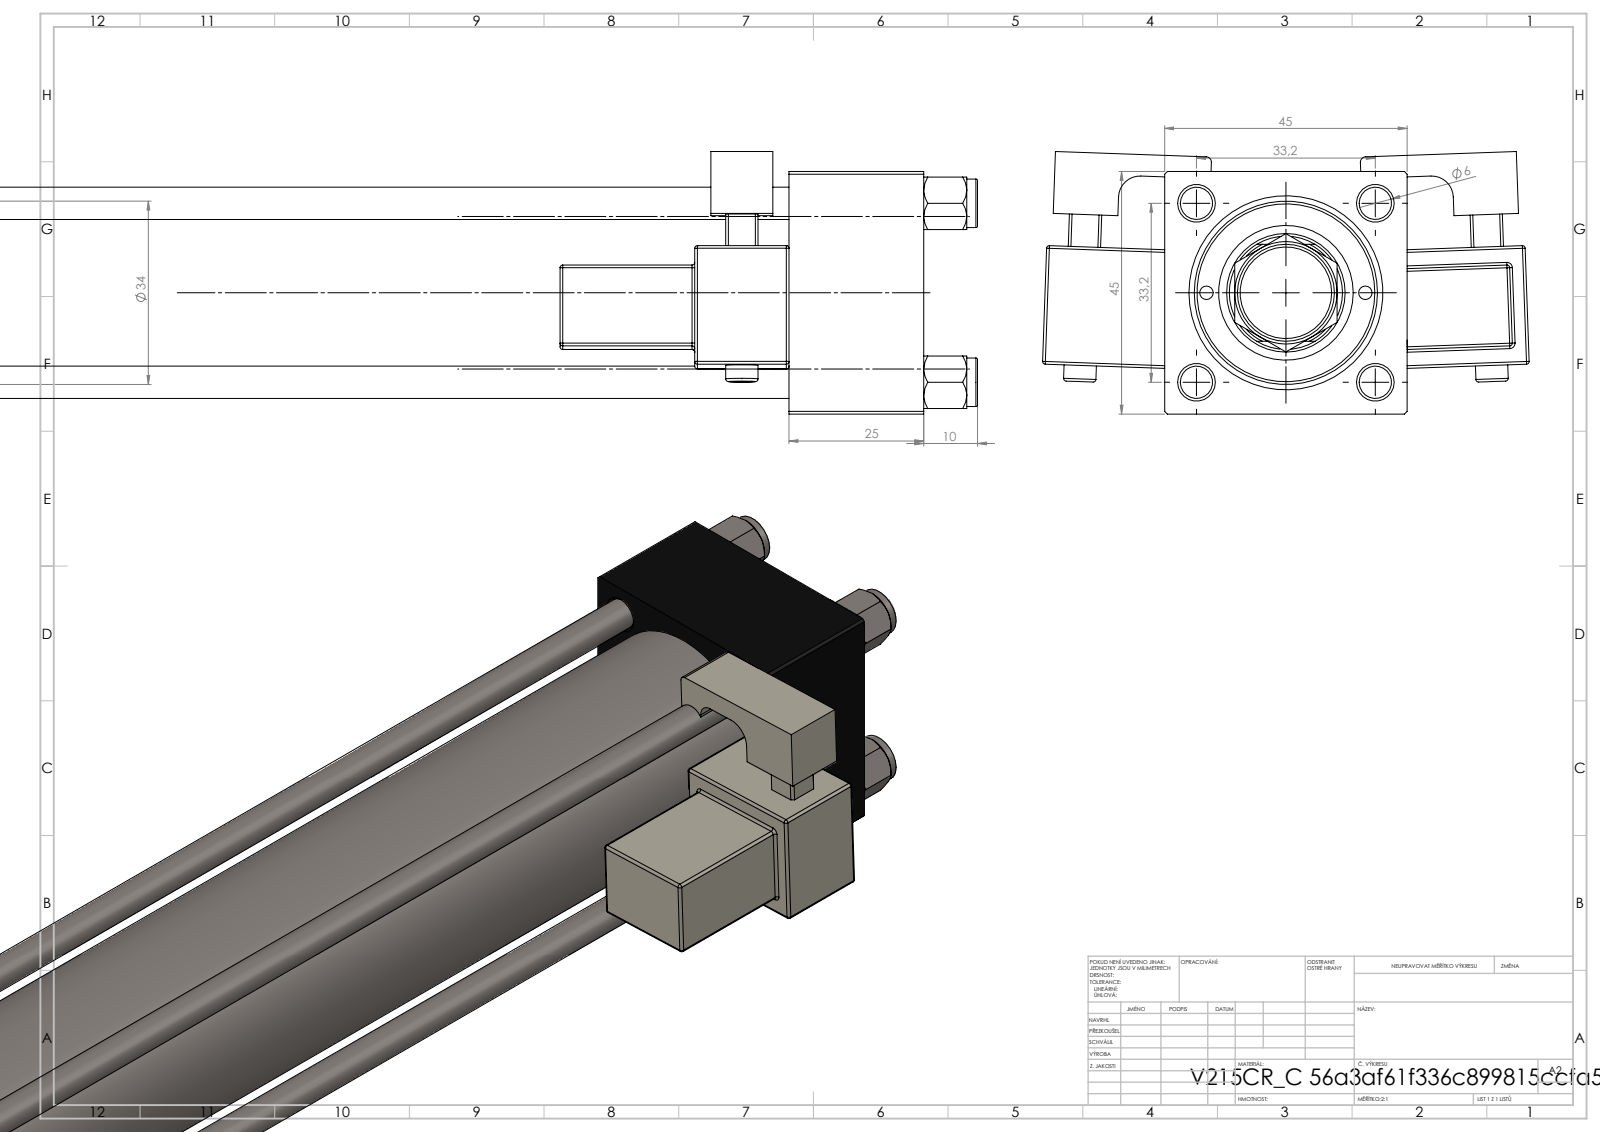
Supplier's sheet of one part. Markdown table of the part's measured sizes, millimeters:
| quantity | value |
| --- | --- |
| part name | V215CR_VCP_C; V215_VC_A; MFA; V215CR_C_TYCINKA (+3 more) |
| STEP written by | SolidWorks 2019 (CONFIG_CONTROL_DESIGN) |
| units | millimeters |
| bodies | 14 solids, 1363 faces (605 planar, 154 cylindrical, 604 other) |
| overall size | 371 × 90.31 × 48.72 |
| volume | 406 576 mm³ |
| surface area | 151 864 mm² |
| round holes (diameter × count) | 6 × 4, 2.5 × 2, 7 × 2, 13.16 × 2, 20 × 2, 10.5 × 1, 22 × 1, 24 × 1, 25 × 1, 32 × 1, 33 × 1 |
| round bosses / shafts (diameter × count) | 9 × 4, 6 × 2, 38 × 1, 34 × 1, 18 × 1, 11 × 1 |
| partial cylindrical surfaces (radius × count) | 0.5 × 48, 1 × 2, 2.5 × 2, 4 × 2, 10.5 × 1 |
| main face-to-face distances | 45, 25, 3, 255, 230, 303, 22.99, 212.5, 278, 13 |
| hole center spacings | 16.7, 23.48, 33.2, 35.47, 14.75, 46.95, 29.5, 255.5 |
